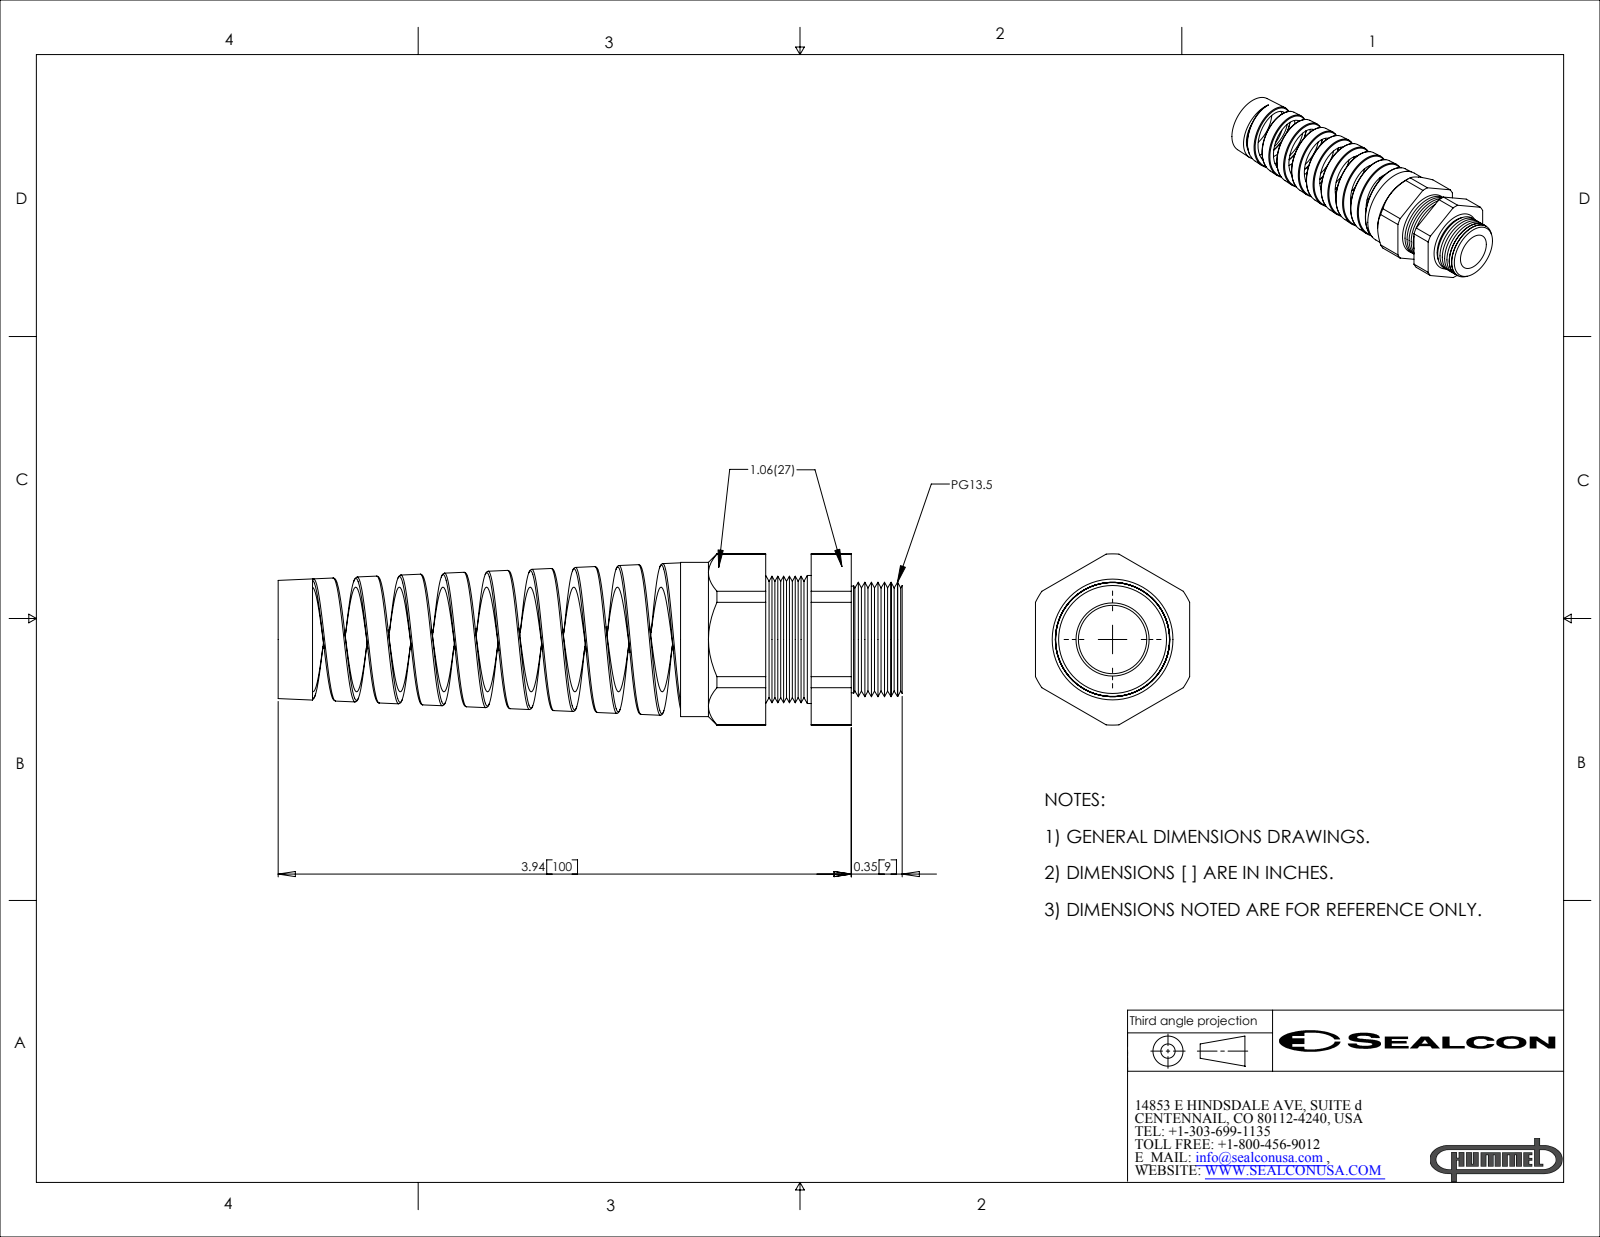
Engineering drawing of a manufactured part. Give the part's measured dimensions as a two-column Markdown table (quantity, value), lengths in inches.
| quantity | value |
| --- | --- |
| part name | CF13GR-BK |
| STEP written by | SolidWorks 2007 (CONFIG_CONTROL_DESIGN) |
| units | inches |
| bodies | 2 solids, 170 faces (24 planar, 43 cylindrical, 103 other) |
| overall size | 4.29 × 1.177 × 1.06 |
| volume | 1.253 in³ |
| surface area | 26.2 in² |
| round holes (diameter × count) | 0.47 × 1, 0.72 × 1 |
| round bosses / shafts (diameter × count) | 1.06 × 1, 0.88 × 1 |
| partial cylindrical surfaces (radius × count) | 0.37 × 1, 0.588 × 1 |
| main face-to-face distances | 1.06, 0.588, 0.313, 0.276, 0.938, 0.626, 0.35, 0.585, 0.898, 1.174 |
